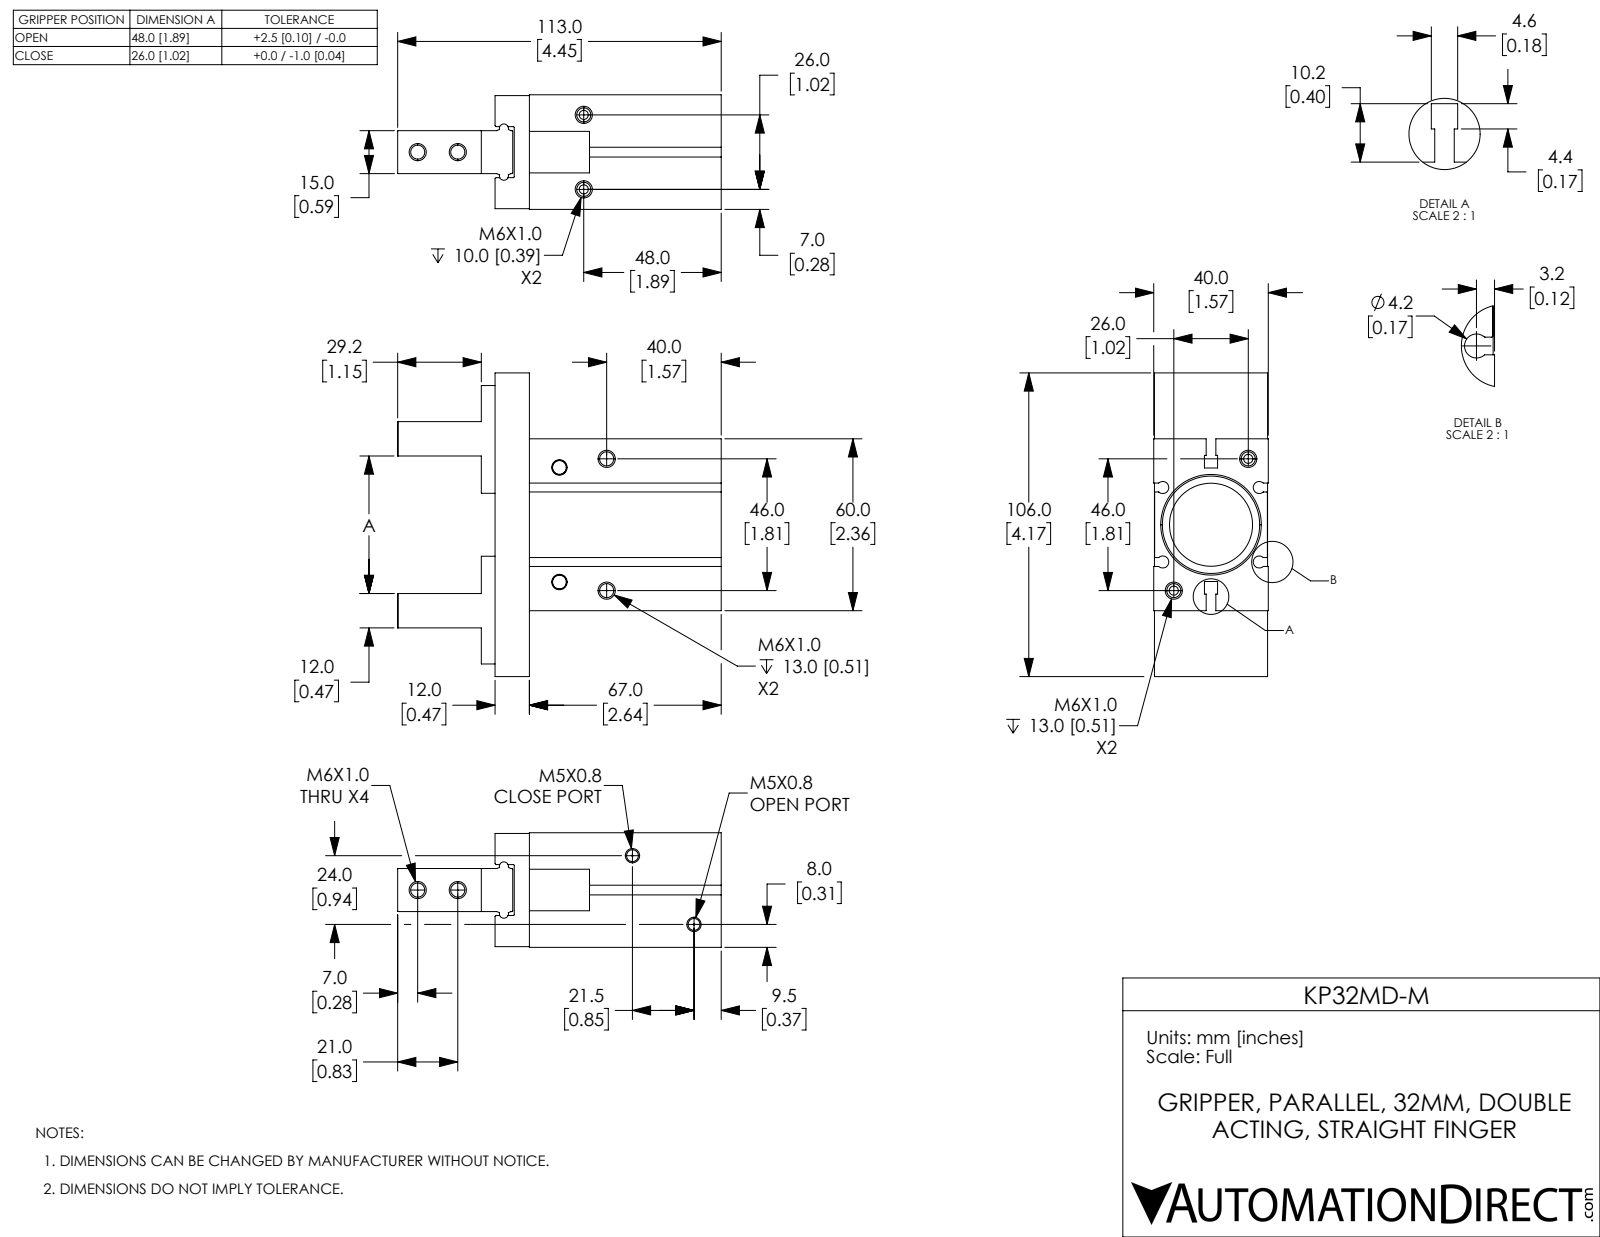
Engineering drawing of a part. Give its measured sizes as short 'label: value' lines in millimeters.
name: KP32MD-M; KP32MD-M-3; KP32MD-M-2; KP32MD-M-1
written by: SolidWorks 2017 (CONFIG_CONTROL_DESIGN)
unit: mm
bodies: 3 solids, 242 faces (118 planar, 62 cylindrical, 62 other)
size: 113 × 106 × 40
volume: 187 147 mm³; area: 45 743 mm²
holes: 4× ⌀4.92, 4× ⌀4.92, 2× ⌀0.5, 2× ⌀4.13, 2× ⌀6.02, 1× ⌀29, 1× ⌀34
rounds: 6× R0.2, 4× R2.1, 2× R0.3, 2× R1.59
face distances: 12.5, 27.25, 39.7, 12, 60, 12.75, 39.75, 39.45, 27, 12.45
hole spacings: 26.42, 45.88, 59.44, 14, 17.03, 26, 30.23, 32.22
